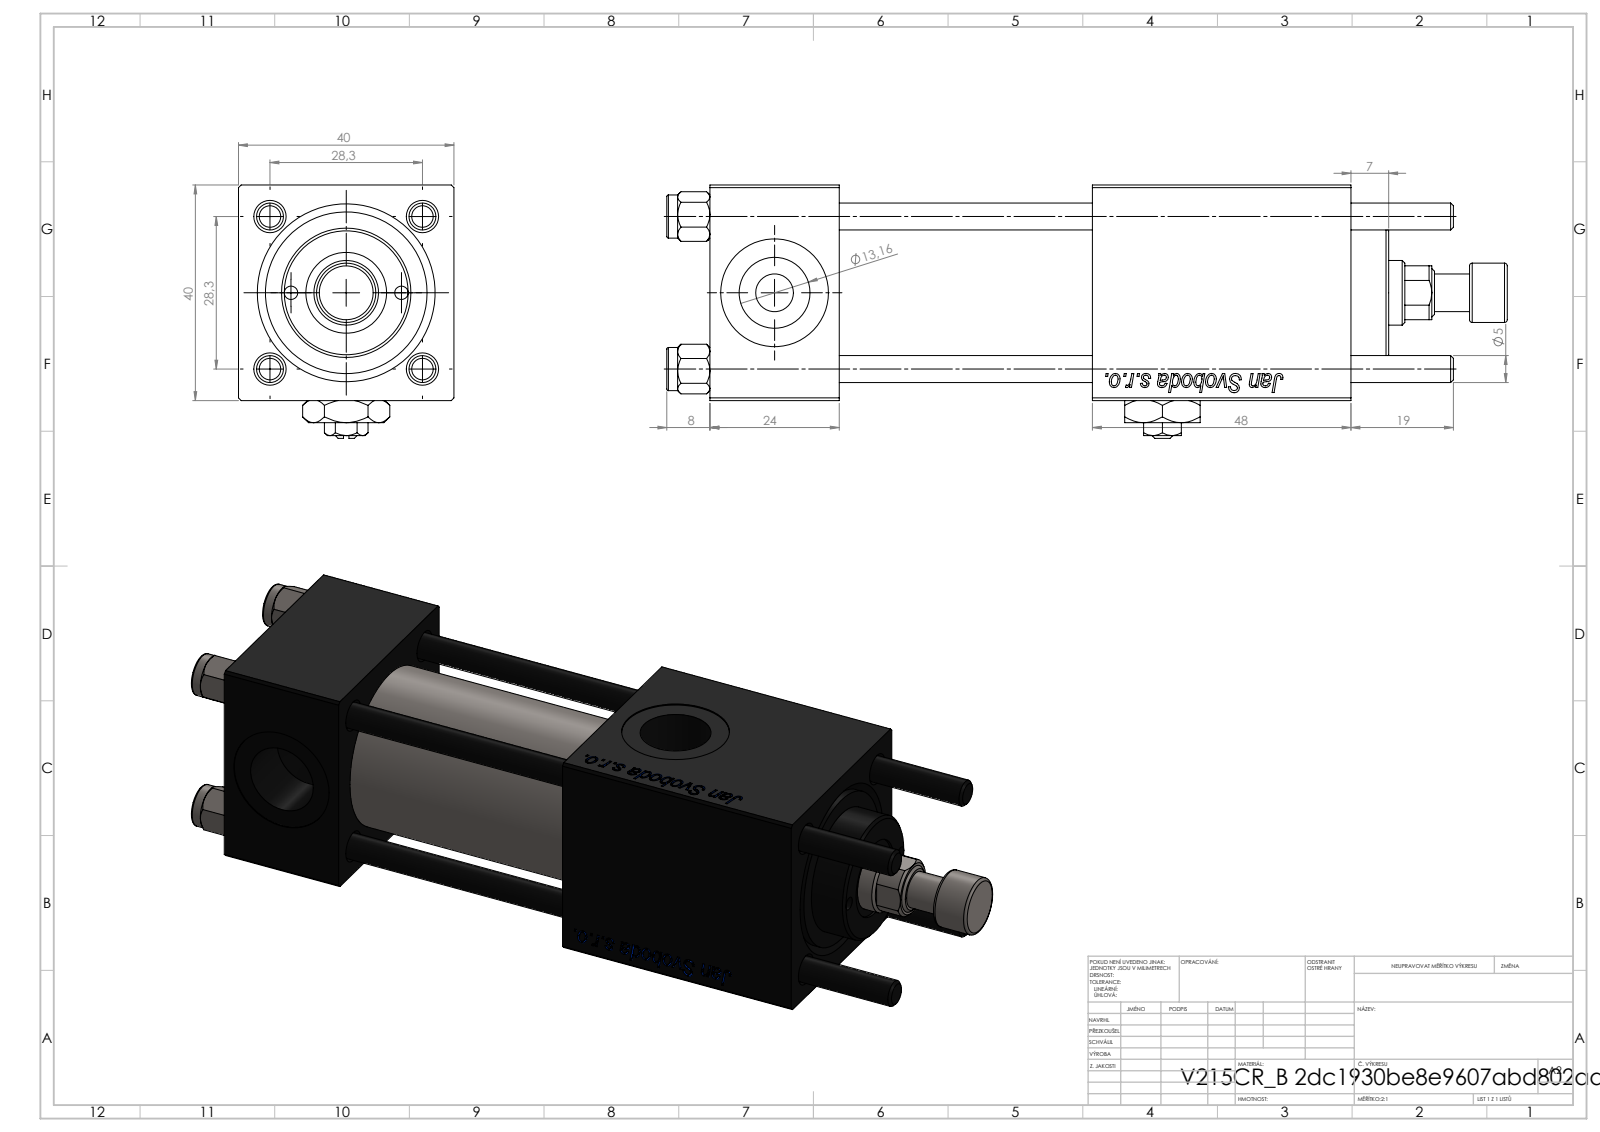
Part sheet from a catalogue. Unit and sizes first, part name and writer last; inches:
Units: inches
Overall size (bounding box): 6.142 × 1.85 × 1.575
Round holes (diameter × count): ⌀0.197 ×4, ⌀0.787 ×4, ⌀0.518 ×3, ⌀0.098 ×2, ⌀0.276 ×2, ⌀0.256 ×1, ⌀0.472 ×1, ⌀0.591 ×1, ⌀0.984 ×1, ⌀1.181 ×1
Round bosses / shafts (diameter × count): ⌀0.315 ×4, ⌀1.22 ×1, ⌀0.945 ×1, ⌀0.433 ×1
Main face-to-face distances: 1.575, 0.945, 1.85, 3.555, 2.61, 2.795, 0.76, 4.685, 3.74, 1.89
Hole centre spacings: 0.578, 0.788, 1.111, 1.114, 0.404, 1.576, 0.807
Volume: 8.852 in³ · Surface area: 93.24 in²
Bodies: 13 solids, 1223 faces (459 planar, 90 cylindrical, 674 other)
Part name (STEP PRODUCT): V215CR_B_TYCINKA; V215CR_ROD_END_F; NUT_M5_B; Zatka_pro_OIL_PORT (+3 more)
STEP written by: SolidWorks 2019 (CONFIG_CONTROL_DESIGN)
